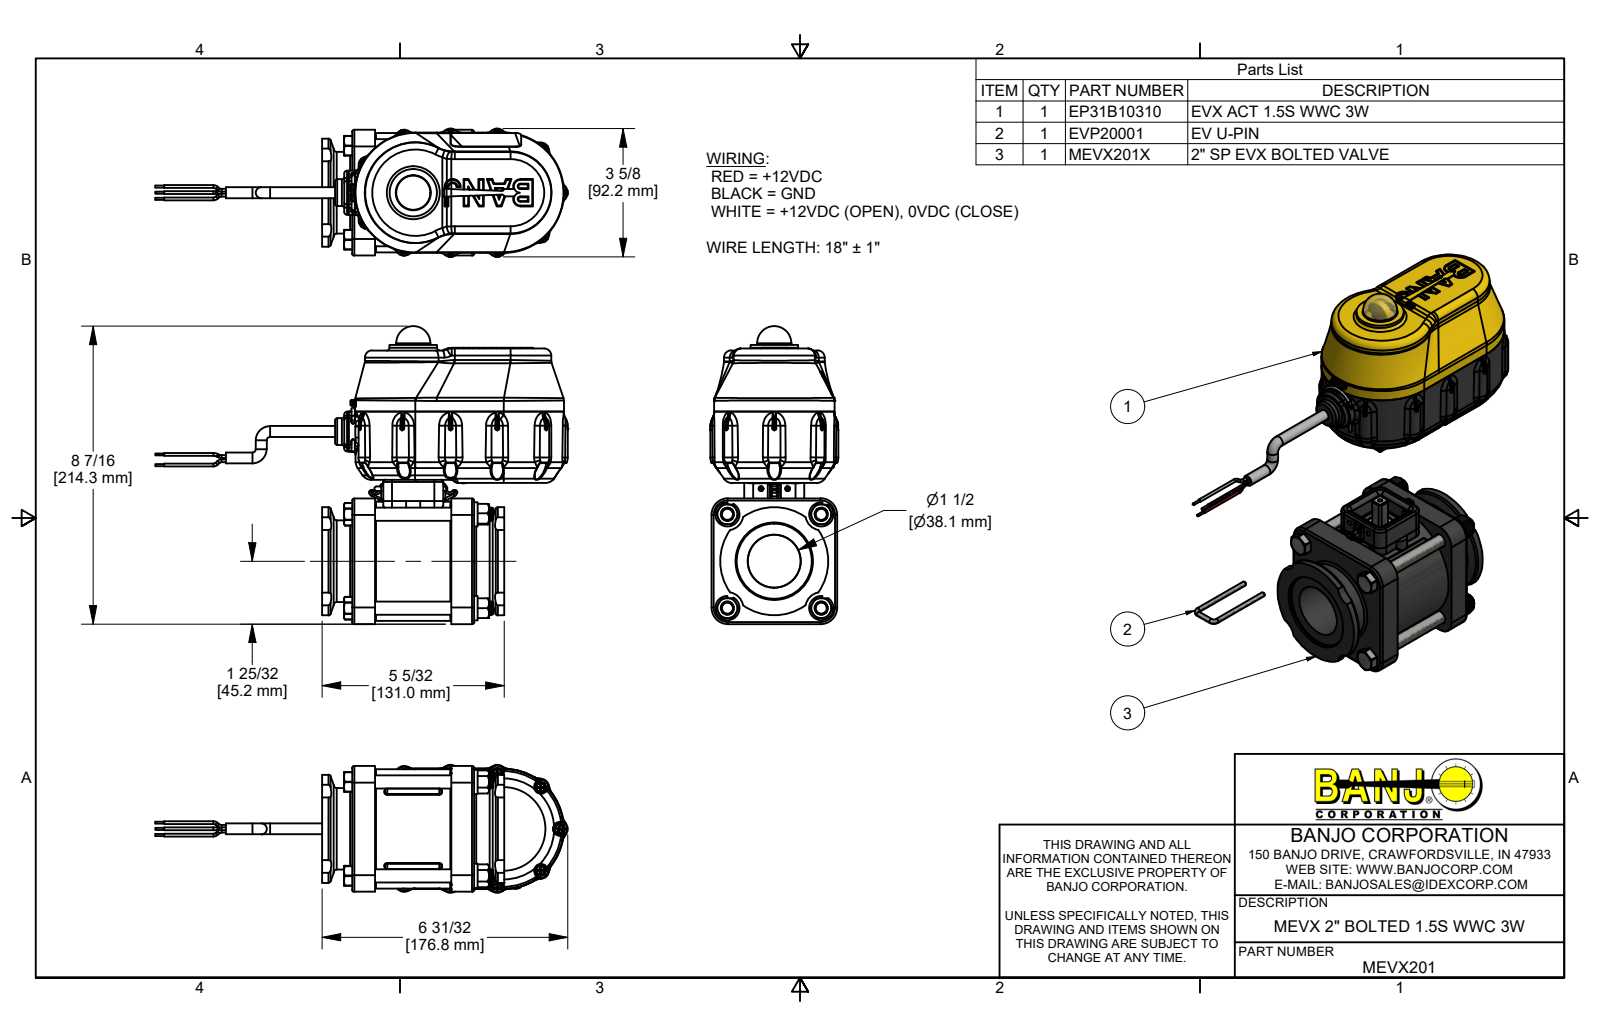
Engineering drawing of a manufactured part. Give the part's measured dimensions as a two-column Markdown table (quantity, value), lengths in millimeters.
| quantity | value |
| --- | --- |
| part name | MEVX201; MEVX201X; MEVX20254A; MEVX20254AX (+8 more) |
| STEP written by | Autodesk Inventor 2019 (AUTOMOTIVE_DESIGN) |
| units | millimeters |
| bodies | 96 solids, 11085 faces (2776 planar, 3349 cylindrical, 4960 other) |
| overall size | 296.8 × 214.3 × 92.2 |
| volume | 1 064 000 mm³ |
| surface area | 422 000 mm² |
| round holes (diameter × count) | 2.4 × 11, 3.8 × 11, 2 × 7, 2.7 × 4, 3.2 × 4, 3.5 × 4, 3.8 × 4, 3.8 × 4, 4.3 × 4, 7.8 × 4, 9.8 × 4, 10.3 × 4 |
| round bosses / shafts (diameter × count) | 8.2 × 60, 6.4 × 17, 2 × 15, 3.6 × 11, 2.7 × 11, 2.2 × 11, 1.5 × 6, 9.5 × 5 |
| partial cylindrical surfaces (radius × count) | 0.3 × 180, 1 × 145, 0.3 × 92, 0.5 × 78, 0.1 × 53, 1.5 × 36, 0.8 × 30, 2 × 28 |
| main face-to-face distances | 2.5, 65.2, 1.5, 16.5, 71.3, 21, 66.9, 4.4, 50.4, 18.5 |
| hole center spacings | 47.8, 67.5, 68.3, 69, 42.2, 45.1, 53, 69.3 |
